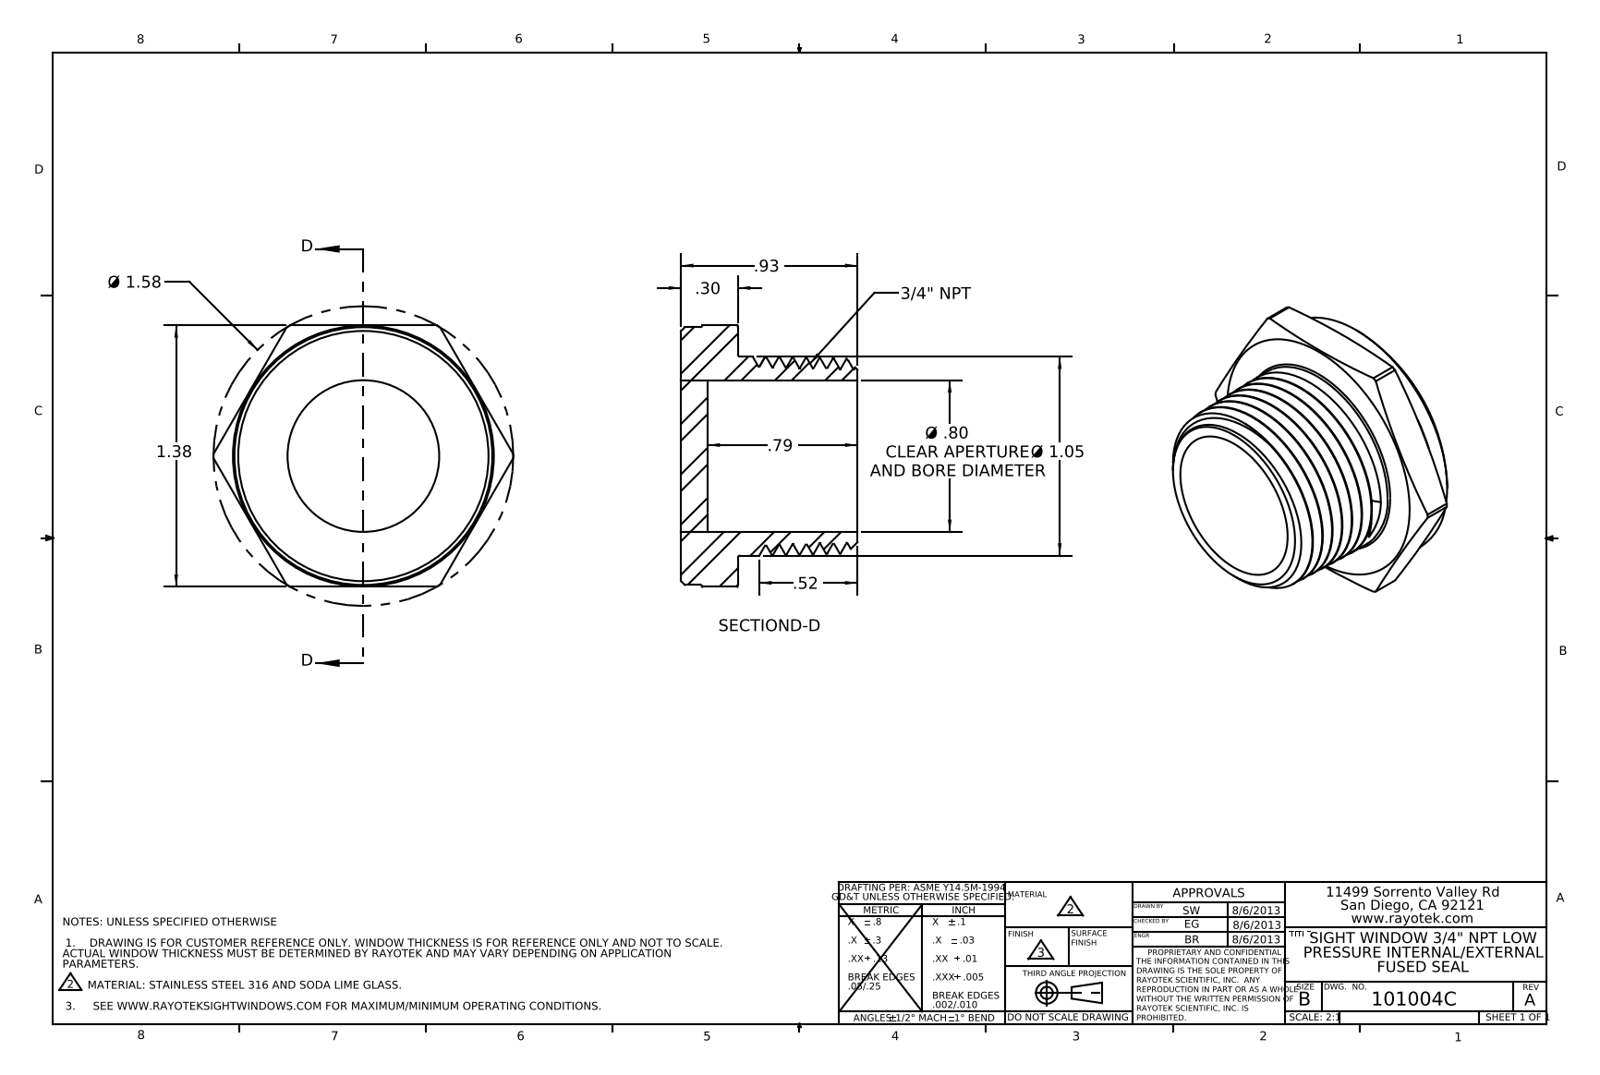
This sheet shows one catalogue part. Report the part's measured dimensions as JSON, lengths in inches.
{"part_name": "403004", "step_written_by": "SolidWorks 2012 (AUTOMOTIVE_DESIGN)", "units": "inches", "bodies": {"solids": 2, "faces": 59, "planar": 14, "cylindrical": 15, "other": 30}, "overall_size": [1.581, 1.38, 0.93], "volume_in3": 0.559, "surface_area_in2": 10.41, "round_holes": [[0.8, 1]], "round_bosses_or_shafts": [[1.36, 1], [1.05, 1]], "partial_cylinders_radius": [[0.791, 1]], "face_to_face_distances": [0.3, 0.14, 0.16, 1.38, 0.93, 0.79, 0.63]}
